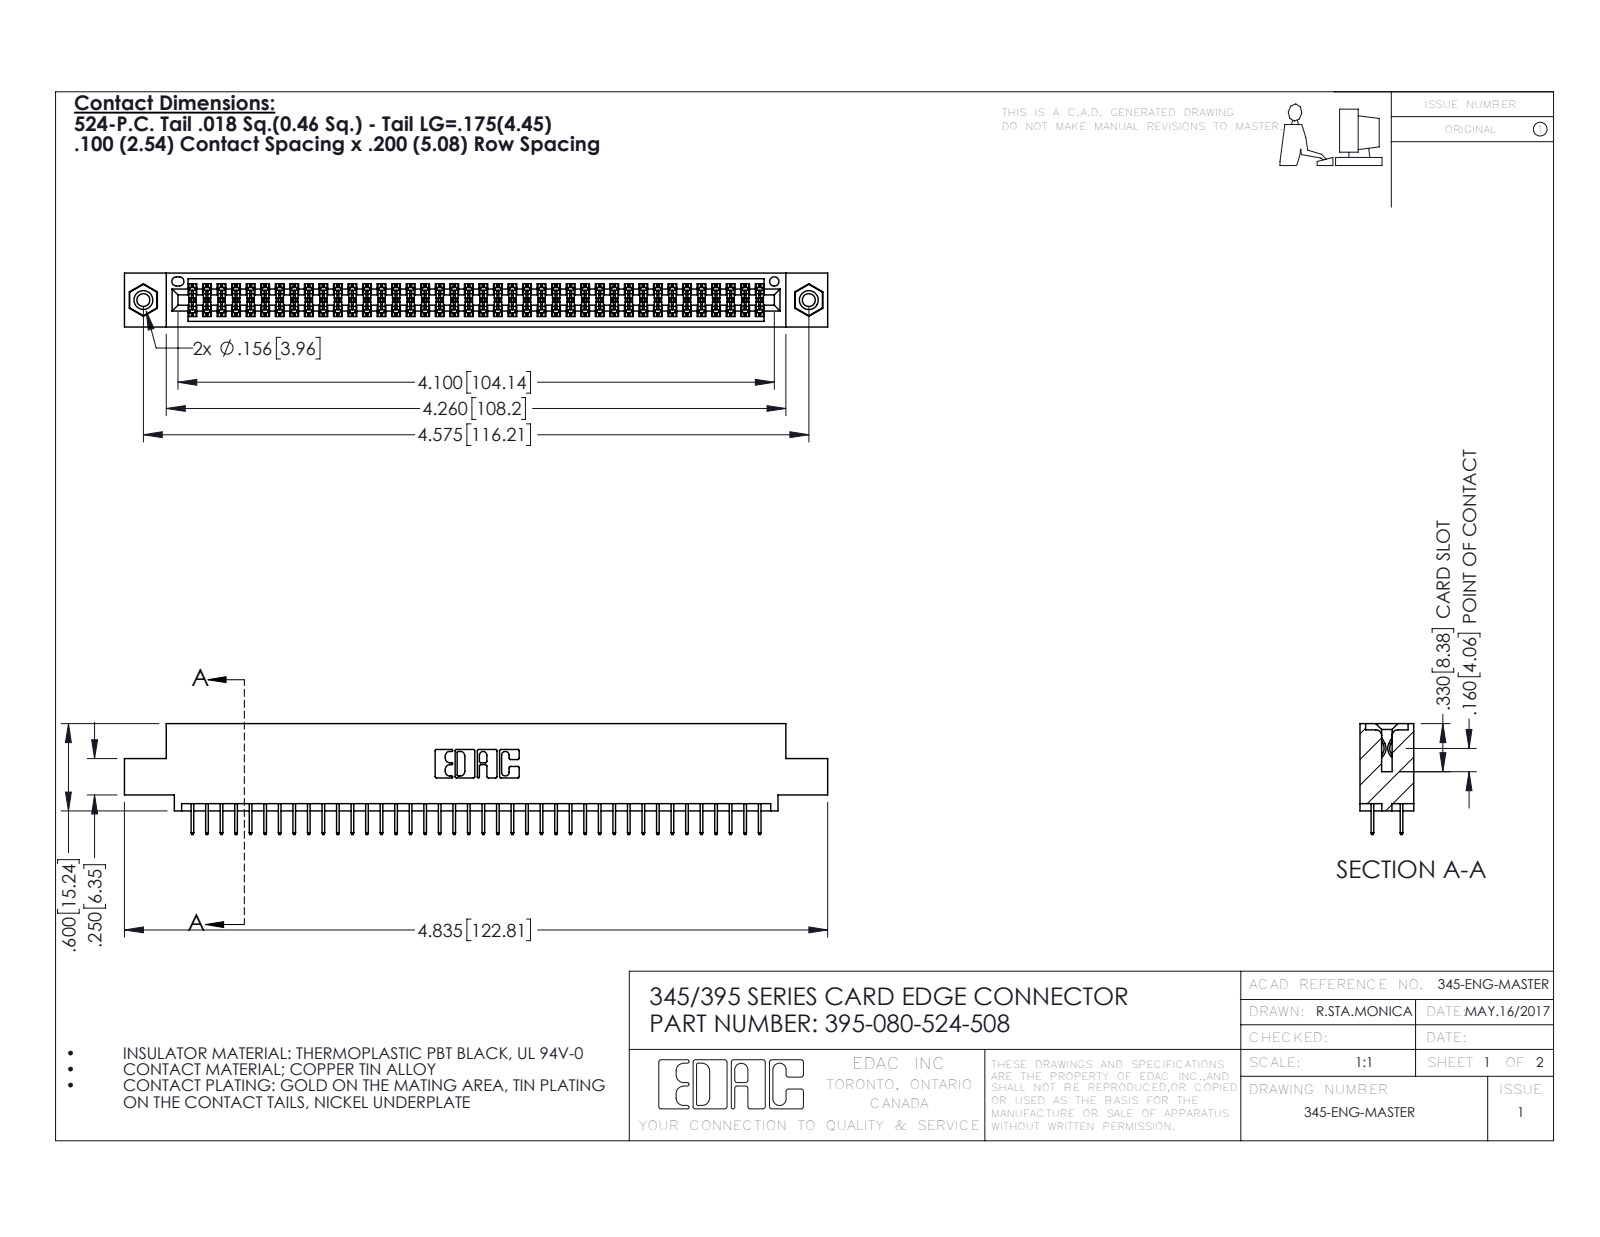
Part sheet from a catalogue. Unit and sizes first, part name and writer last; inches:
Units: inches
Overall size (bounding box): 4.835 × 0.762 × 0.37
Round holes (diameter × count): ⌀0.089 ×2, ⌀0.125 ×2, ⌀0.156 ×2, ⌀0.064 ×1
Round bosses / shafts (diameter × count): ⌀0.155 ×2
Partial cylindrical surfaces — rounded edges, fillets, slot ends (radius × count): R0.006 ×120, R0.01 ×22, R0.007 ×6, R0.031 ×6, R0.026 ×3, R0.014 ×2, R0.019 ×2, R0.022 ×2
Main face-to-face distances: 0.072, 0.298, 0.2, 0.37, 0.098, 0.272, 0.025, 0.225, 0.072, 0.175
Hole centre spacings: 0.27, 4.339, 4.575
Volume: 0.715 in³ · Surface area: 26.44 in²
Bodies: 83 solids, 4510 faces (3236 planar, 1258 cylindrical, 16 other)
Part name (STEP PRODUCT): 395-080-524-508; 345-292-001_345-293-124; 345-250-001_345-250-003-102; 345 Part_0.110 Offset - 0.156 Dia-TI
STEP written by: SolidWorks 2016 (CONFIG_CONTROL_DESIGN)
